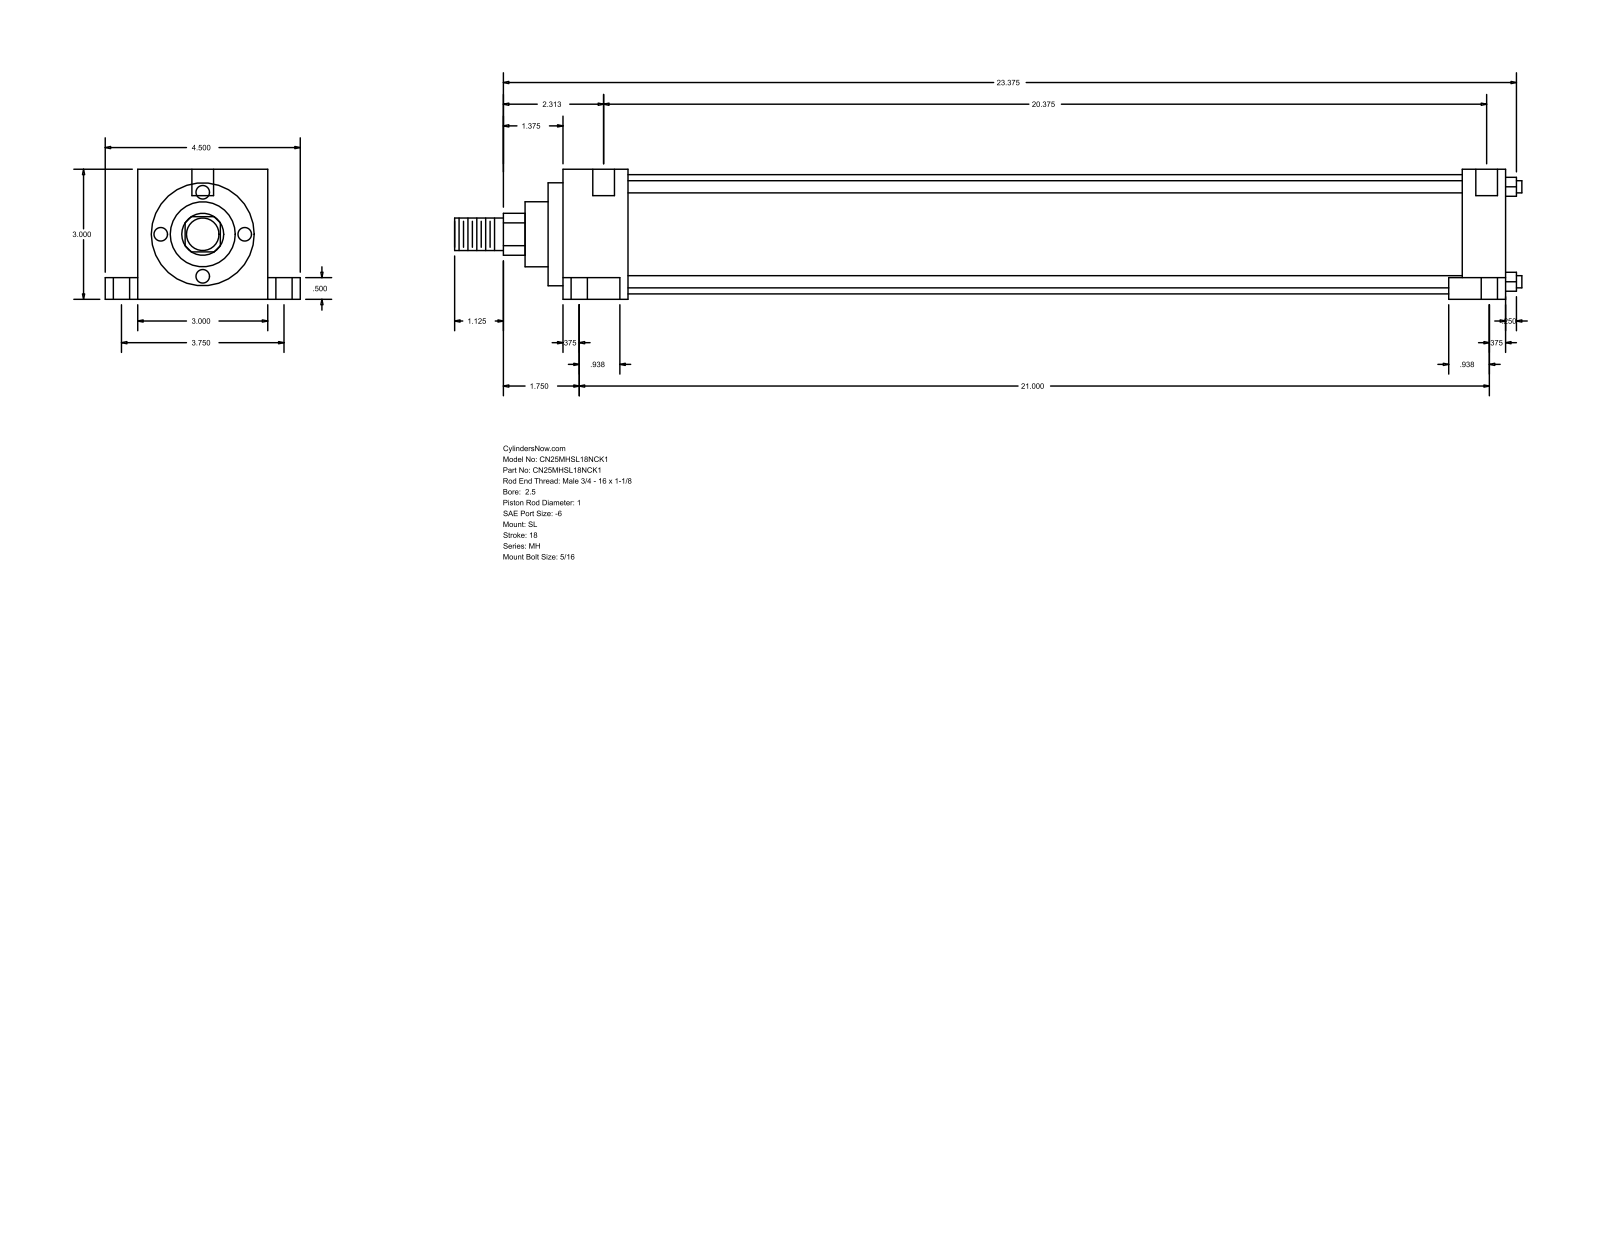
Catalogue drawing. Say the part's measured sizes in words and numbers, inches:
The part is named "MH_SL__0250_1". Its 3-D file was written by "GSSL Pune (CONFIG_CONTROL_DESIGN)". It is 0 solids with 86 faces: 61 planar, 25 cylindrical and 0 other. Overall it measures 24.625 by 4.5 by 3 inches. Round holes: 2 of diameter 0.219, 2 of diameter 0.375, 2 of diameter 0.625, 1 of diameter 0.5. Round bosses or shafts: 4 of diameter 0.281, 1 of diameter 2.75, 1 of diameter 2.375, 1 of diameter 1.5, 1 of diameter 1, 1 of diameter 0.75. Partial cylindrical surfaces (rounded edges, fillets, slot ends): 1 of radius 0.484. The main face-to-face distances are 3, 1, 21.094, 22.094, 0.5, 2.5, 0.75, 3.75, 0.531, 21.625. The hole center spacings are 1.876, 0.125, 3.75.
